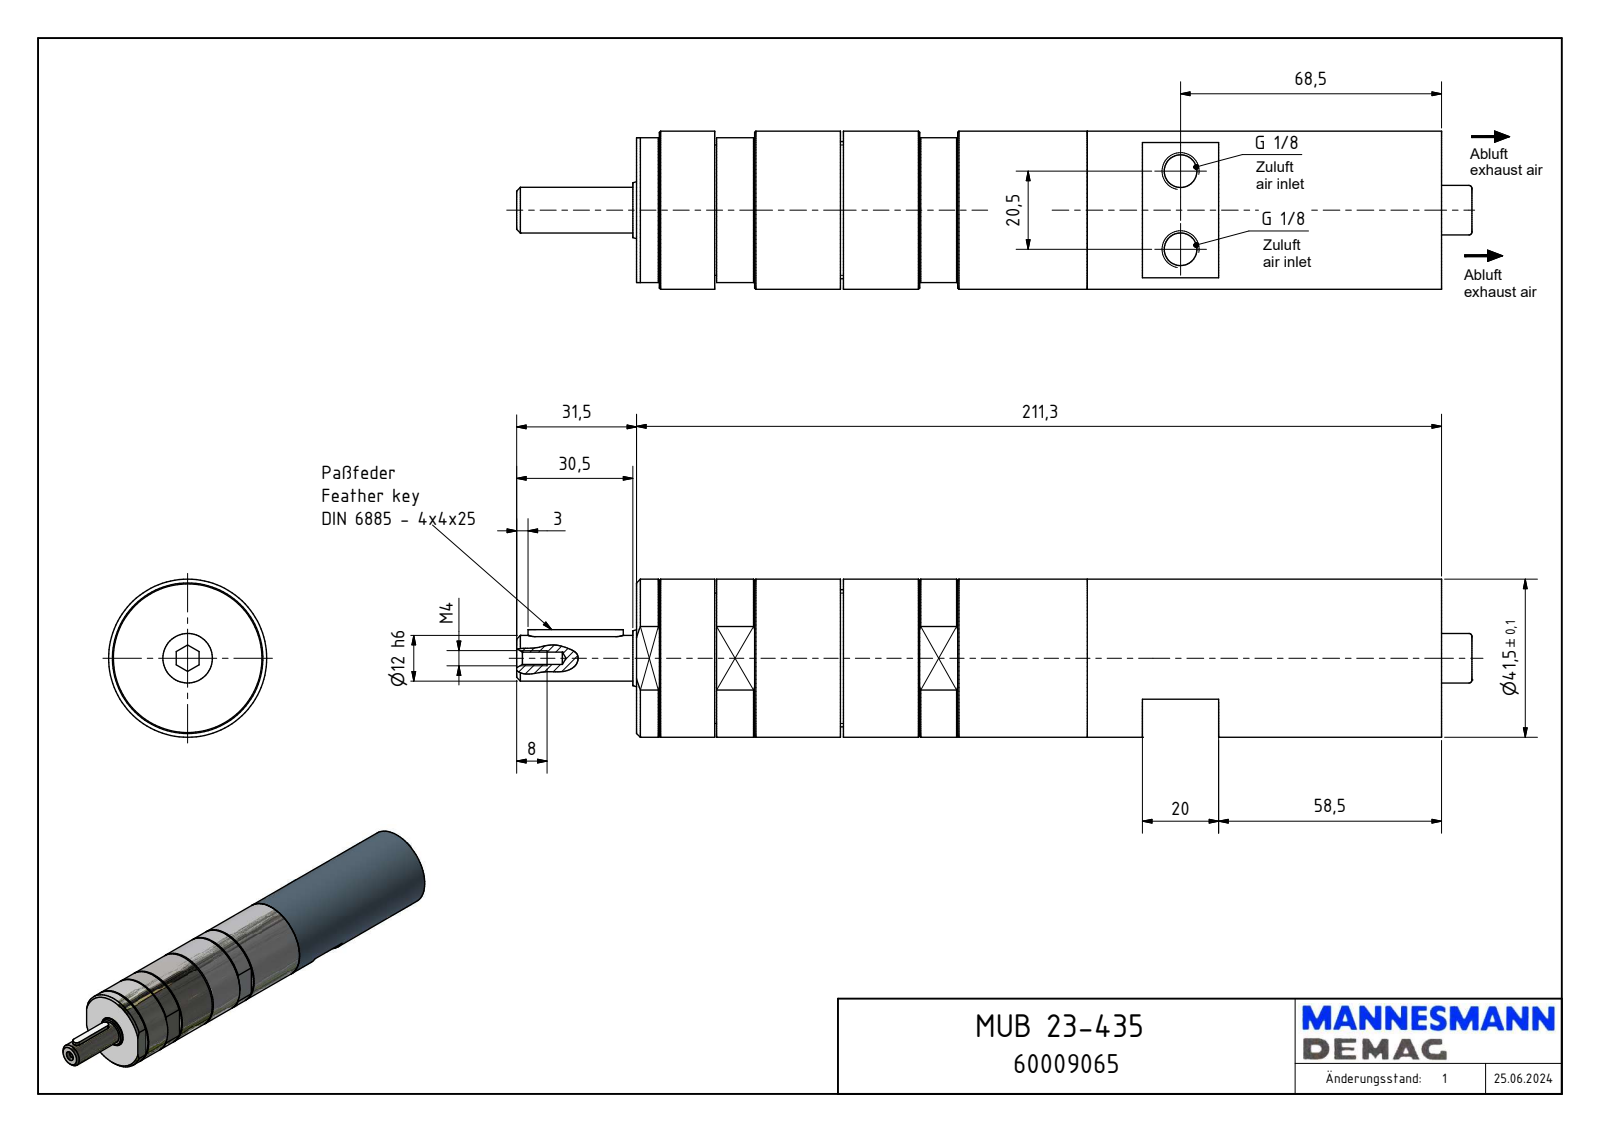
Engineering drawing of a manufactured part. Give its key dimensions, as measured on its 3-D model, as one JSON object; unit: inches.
{"part_name": "MUB 23-435_60009065", "step_written_by": "Autodesk Inventor 2018 (AUTOMOTIVE_DESIGN)", "units": "inches", "bodies": {"solids": 1, "faces": 136, "planar": 62, "cylindrical": 50, "other": 24}, "overall_size": [9.85, 1.634, 1.634], "volume_in3": 17.17, "surface_area_in2": 55.91, "round_holes": [[0.337, 2], [0.128, 1], [0.335, 1], [0.512, 1], [0.63, 1], [1.555, 1]], "round_bosses_or_shafts": [[1.634, 1], [1.535, 1], [1.417, 1], [0.589, 1], [0.472, 1], [0.315, 1]], "partial_cylinders_radius": [[0.079, 4], [0.039, 2], [0.063, 2], [0.098, 2], [0.319, 1], [0.489, 1]], "face_to_face_distances": [8.295, 3.091, 1.496, 2.106, 6.189, 2.114, 6.181, 2.303, 0.787, 5.992], "hole_center_spacings": [0.807]}
